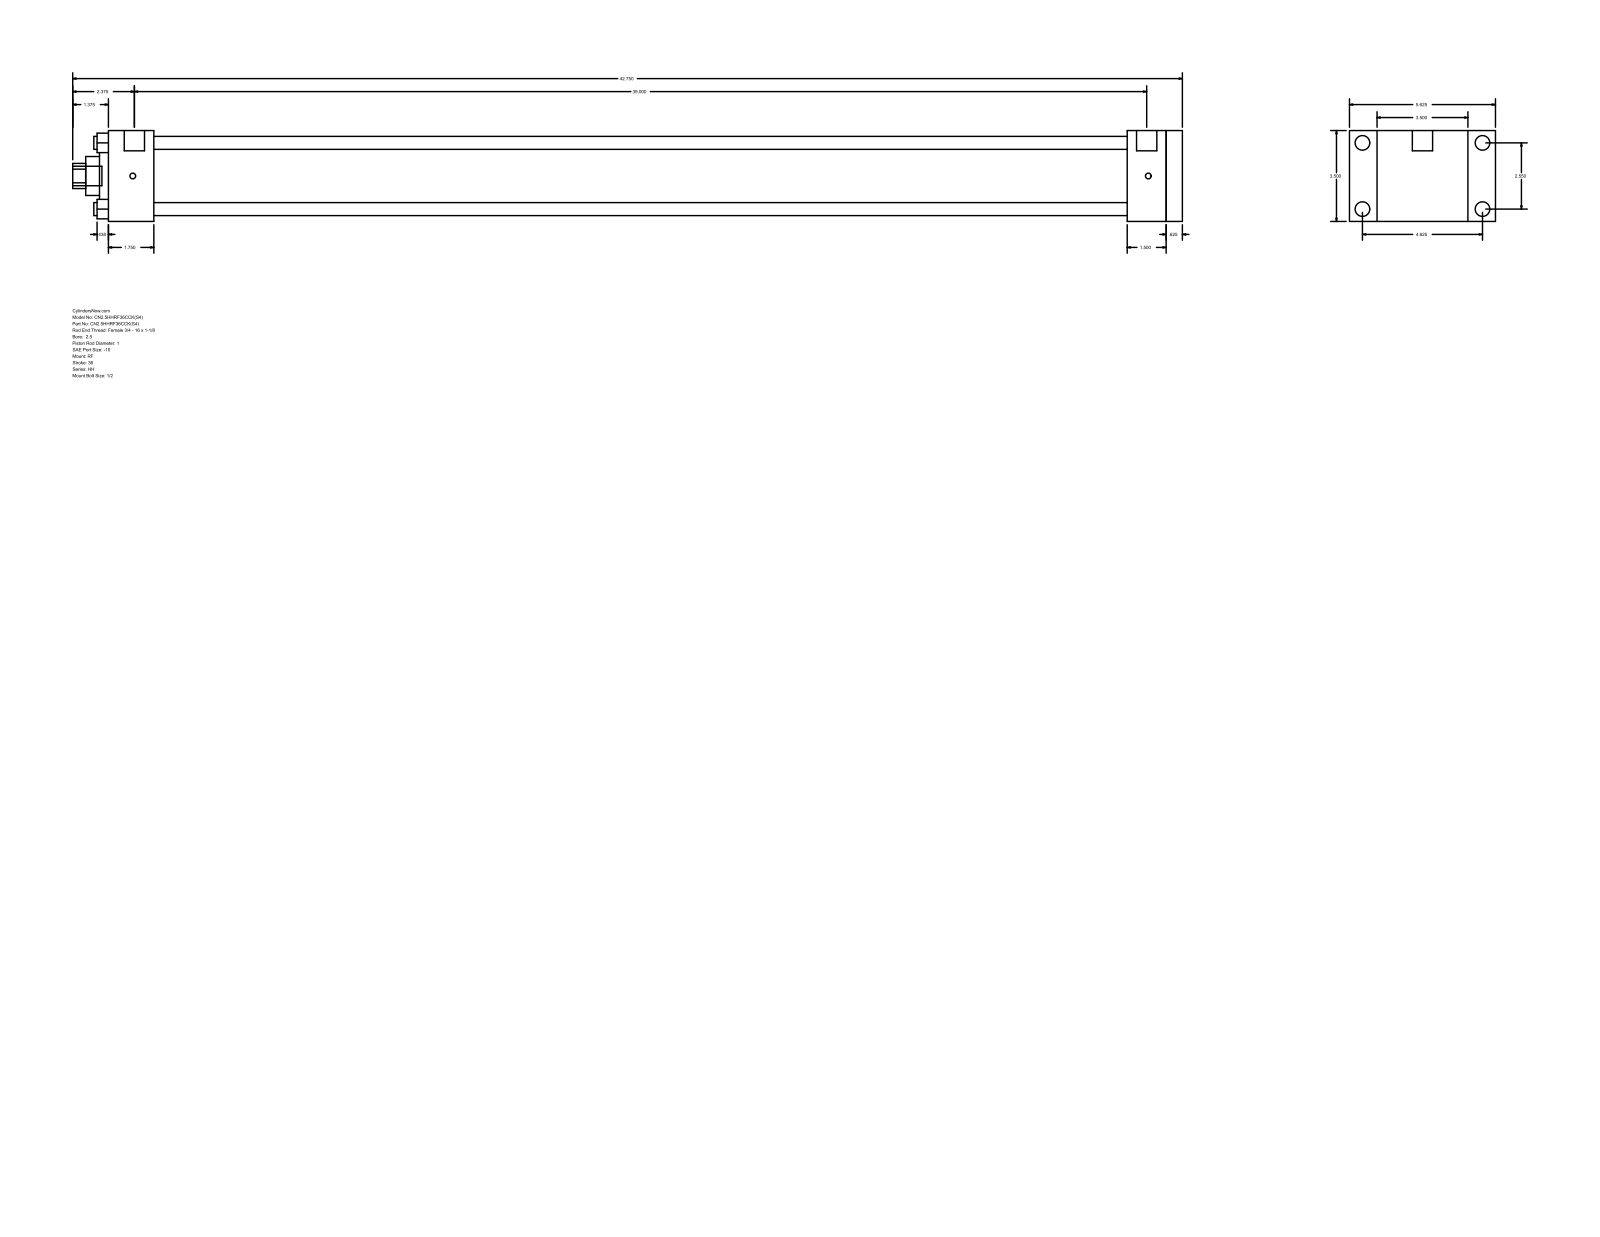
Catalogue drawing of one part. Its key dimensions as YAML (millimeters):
part_name: "HH_RF__0250_1"
step_written_by: "GSSL Pune (CONFIG_CONTROL_DESIGN)"
units: millimeters
bodies: {solids: 0, faces: 94, planar: 65, cylindrical: 29, other: 0}
overall_size: [1085.85, 142.88, 88.9]
round_holes:
  - {diameter: 12.7, count: 4}
  - {diameter: 25.4, count: 1}
  - {diameter: 38.1, count: 1}
  - {diameter: 60.33, count: 1}
  - {diameter: 73.03, count: 1}
round_bosses_or_shafts:
  - {diameter: 14.3, count: 4}
  - {diameter: 5.56, count: 4}
  - {diameter: 19.84, count: 2}
  - {diameter: 19.05, count: 1}
partial_cylinders:
  - {radius: 12.29, count: 1}
face_to_face_distances: [88.9, 15.88, 1035.05, 1050.93, 44.46, 990.59, 1006.47, 996.96, 952.5, 38.09]
hole_center_spacings: [45.79, 64.76, 91.58]
